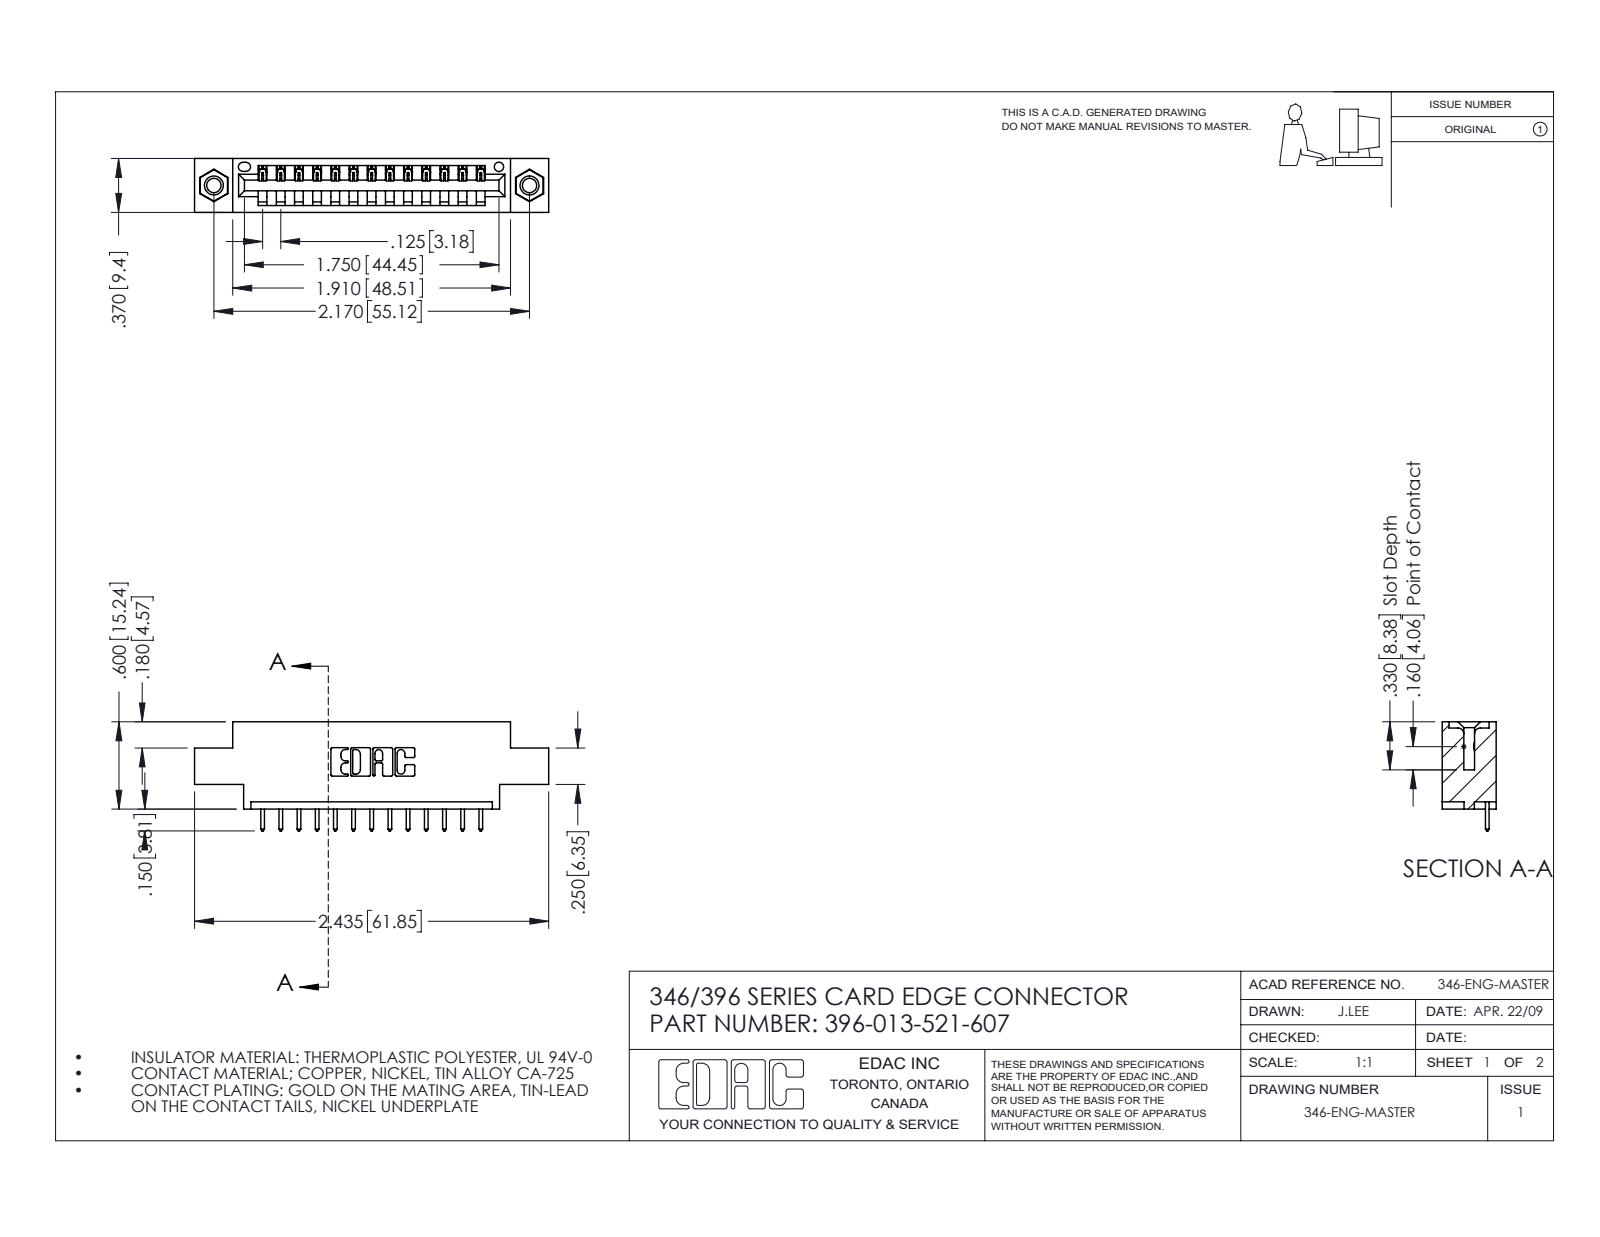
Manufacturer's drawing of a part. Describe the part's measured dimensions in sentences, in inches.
The part is named "346 Part_0.170 Offset - 0.156 Dia-TI; 345-292-001_345-293-121; 345-250-001_345-250-005-103; 396-013-521-607". Its 3-D file was written by "SolidWorks 2016 (CONFIG_CONTROL_DESIGN)". It is 16 solids with 940 faces: 632 planar, 292 cylindrical and 16 other. Overall it measures 2.435 by 0.75 by 0.37 inches. Its volume is 0.337 cubic inches and its surface area 10.27 square inches. Round holes: 2 of diameter 0.098, 2 of diameter 0.125, 2 of diameter 0.156, 1 of diameter 0.064. Round bosses or shafts: 2 of diameter 0.155. Partial cylindrical surfaces (rounded edges, fillets, slot ends): 26 of radius 0.006, 26 of radius 0.01, 22 of radius 0.01, 6 of radius 0.007, 6 of radius 0.031, 3 of radius 0.026, 2 of radius 0.031, 2 of radius 0.04. The main face-to-face distances are 0.37, 0.25, 0.048, 0.322, 0.222, 0.148, 0.072, 0.298, 0.025, 0.1. The hole center spacings are 0.246, 1.964, 2.17.
